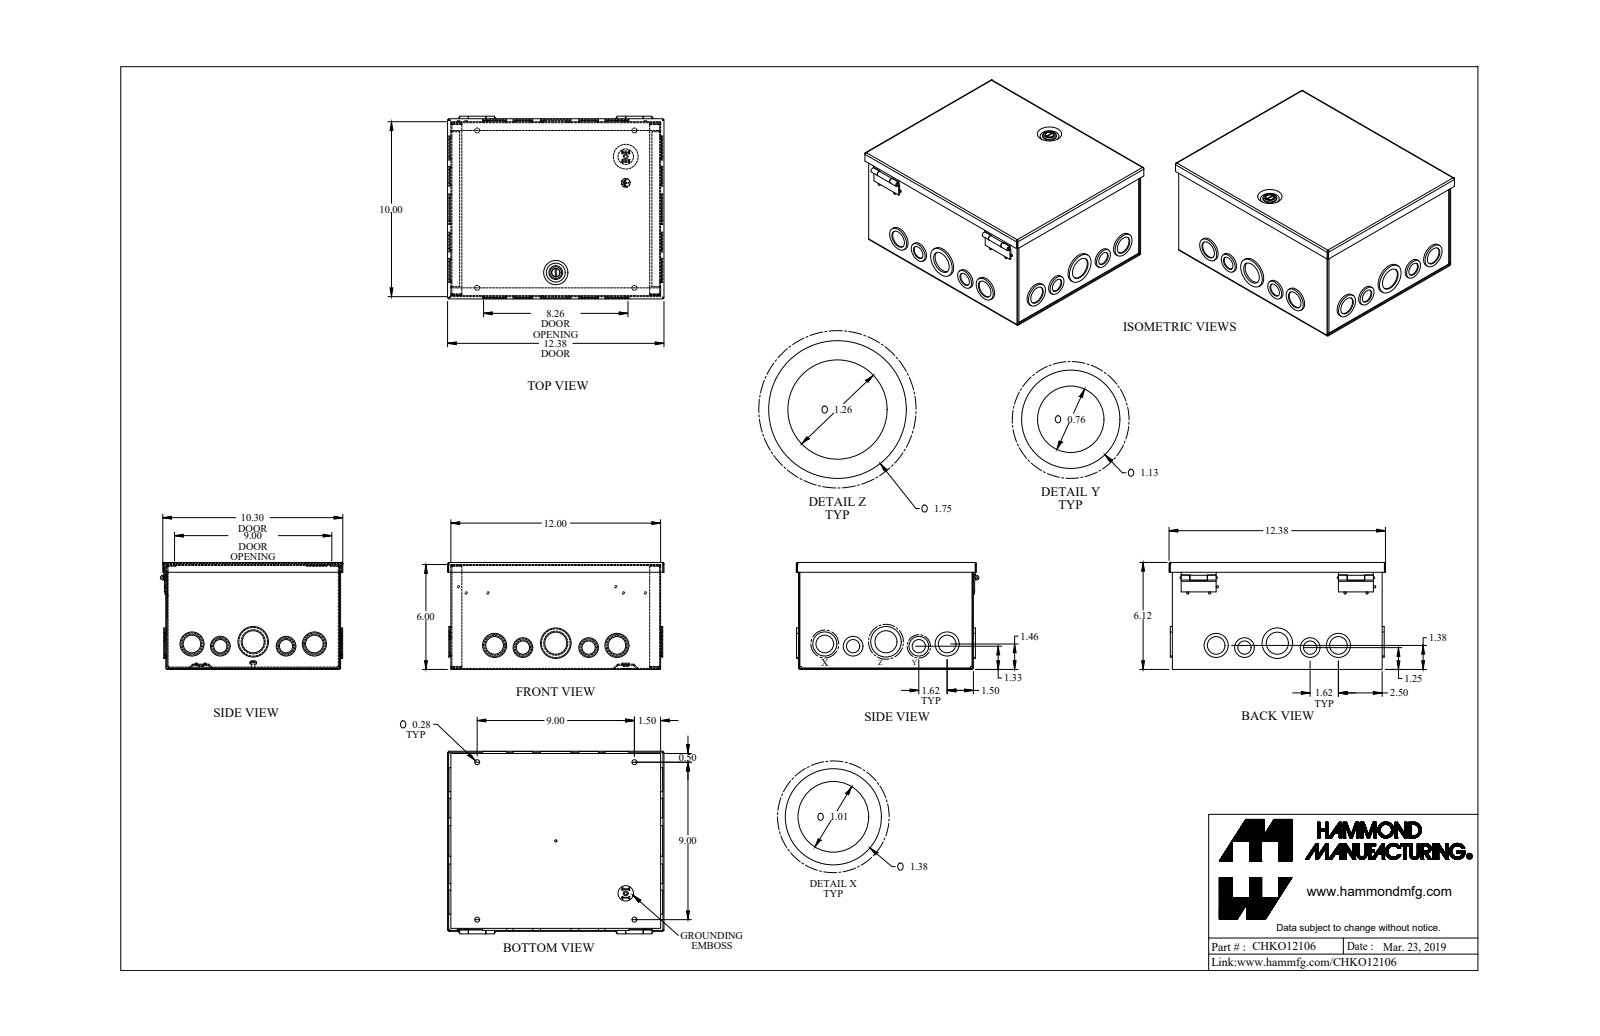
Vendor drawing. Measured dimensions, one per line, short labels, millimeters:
name: CHKO12106_Default
written by: SolidWorks 2019 (CONFIG_CONTROL_DESIGN)
unit: mm
bodies: 12 solids, 727 faces (352 planar, 332 cylindrical, 43 other)
size: 314.5 × 265.3 × 155.4
volume: 559 600 mm³; area: 776 100 mm²
holes: 8× ⌀25.7, 6× ⌀32, 4× ⌀7.1, 4× ⌀19.3, 2× ⌀41.6, 1× ⌀3.2, 1× ⌀4.3, 1× ⌀8.1, 1× ⌀12.1, 1× ⌀12.7
bosses: 8× ⌀3.3, 6× ⌀28.6, 4× ⌀22.2, 4× ⌀22.2, 3× ⌀34.9, 3× ⌀34.9, 2× ⌀44.5, 2× ⌀28.6
rounds: 16× R0.7, 16× R2.2, 8× R1.4, 4× R0.3, 4× R2.5, 2× R0.9, 2× R2, 2× R6.4
face distances: 1.4, 153.9, 252.6, 155.4, 152.5, 303.4, 254, 251.1, 304.8, 301.9
hole spacings: 41.3, 48.2, 89, 136.7, 228.6, 95.5, 177.8, 323.3
